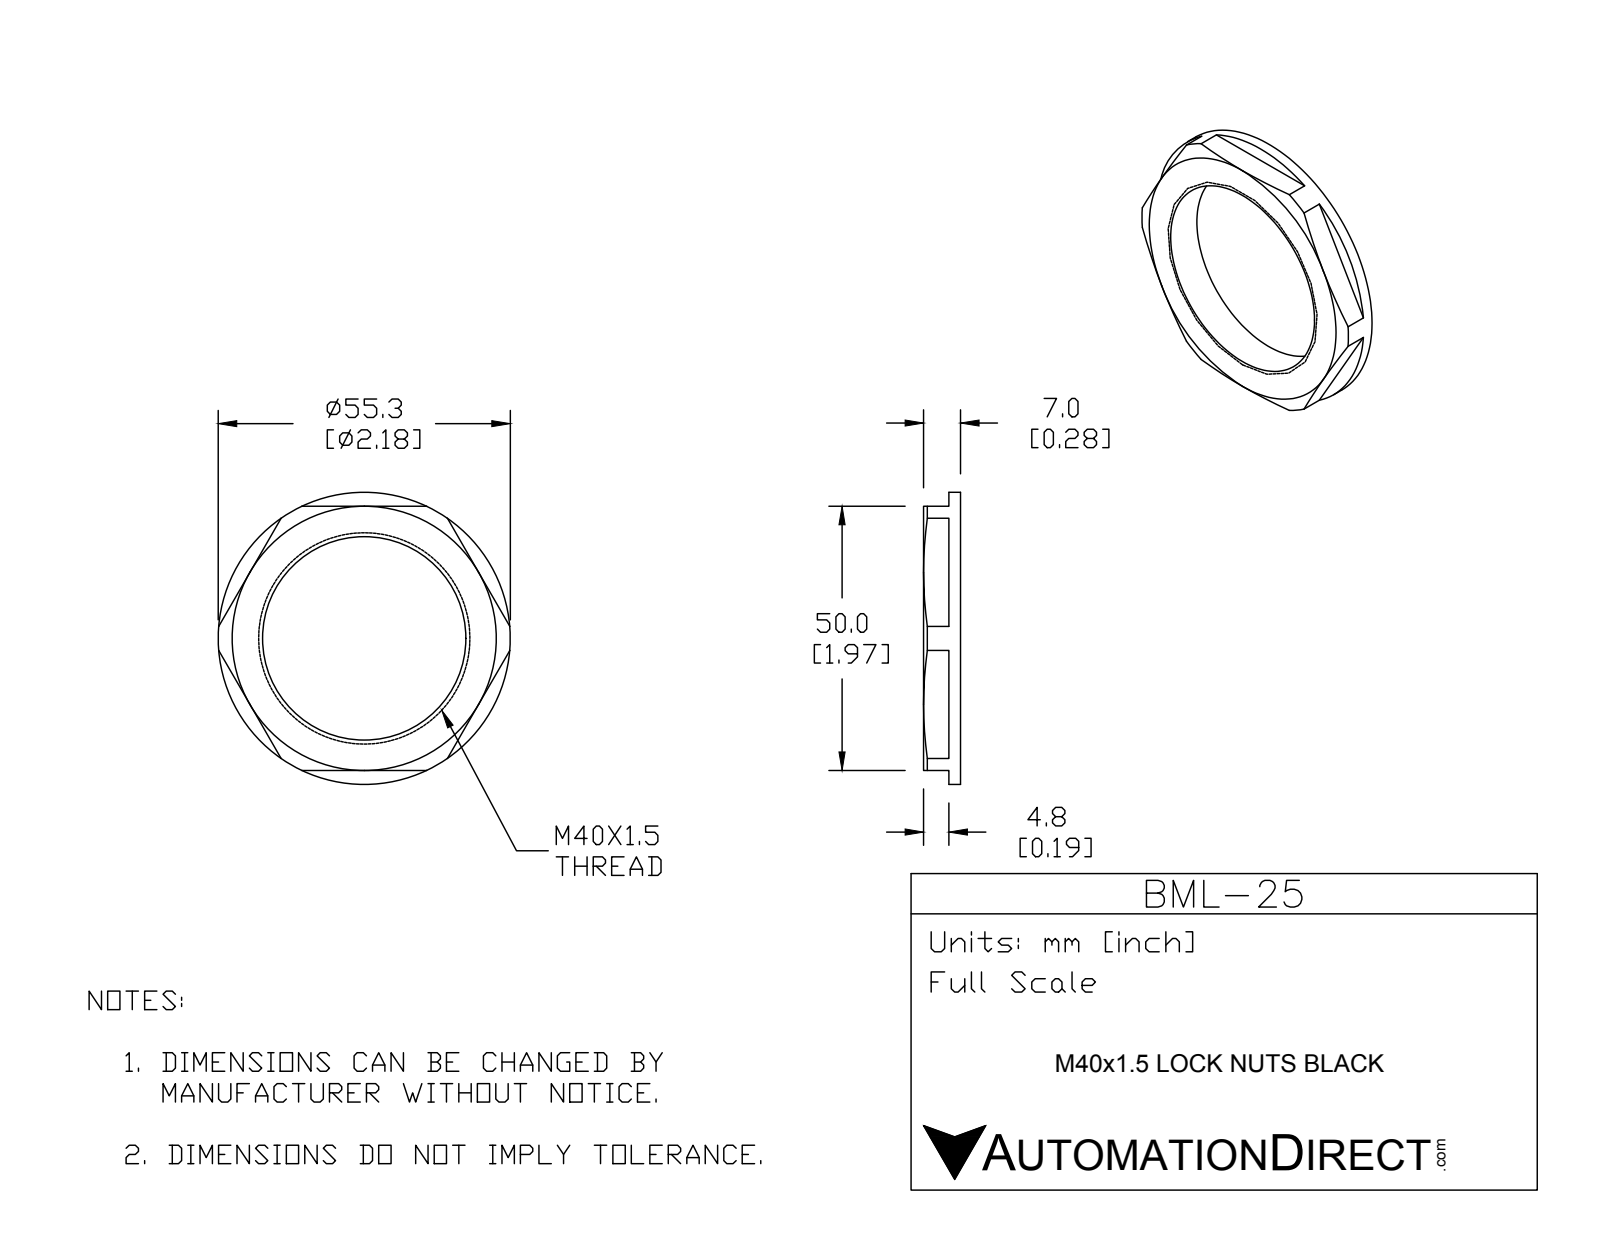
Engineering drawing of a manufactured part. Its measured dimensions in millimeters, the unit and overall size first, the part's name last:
Units: millimetres
Overall size (bounding box): 55.3 × 55.3 × 7
Round holes (diameter × count): ⌀1.5 ×3, ⌀38.5 ×1
Round bosses / shafts (diameter × count): ⌀55.3 ×1
Main face-to-face distances: 7, 50, 2.2, 4.8, 1.9, 6.7
Hole centre spacings: 26.2, 45.38
Volume: 7 398 mm³ · Surface area: 4 473 mm²
Bodies: 1 solid, 33 faces (17 planar, 10 cylindrical, 6 other)
Part name (STEP PRODUCT): BML-25
STEP written by: SolidWorks 2015 (CONFIG_CONTROL_DESIGN)
